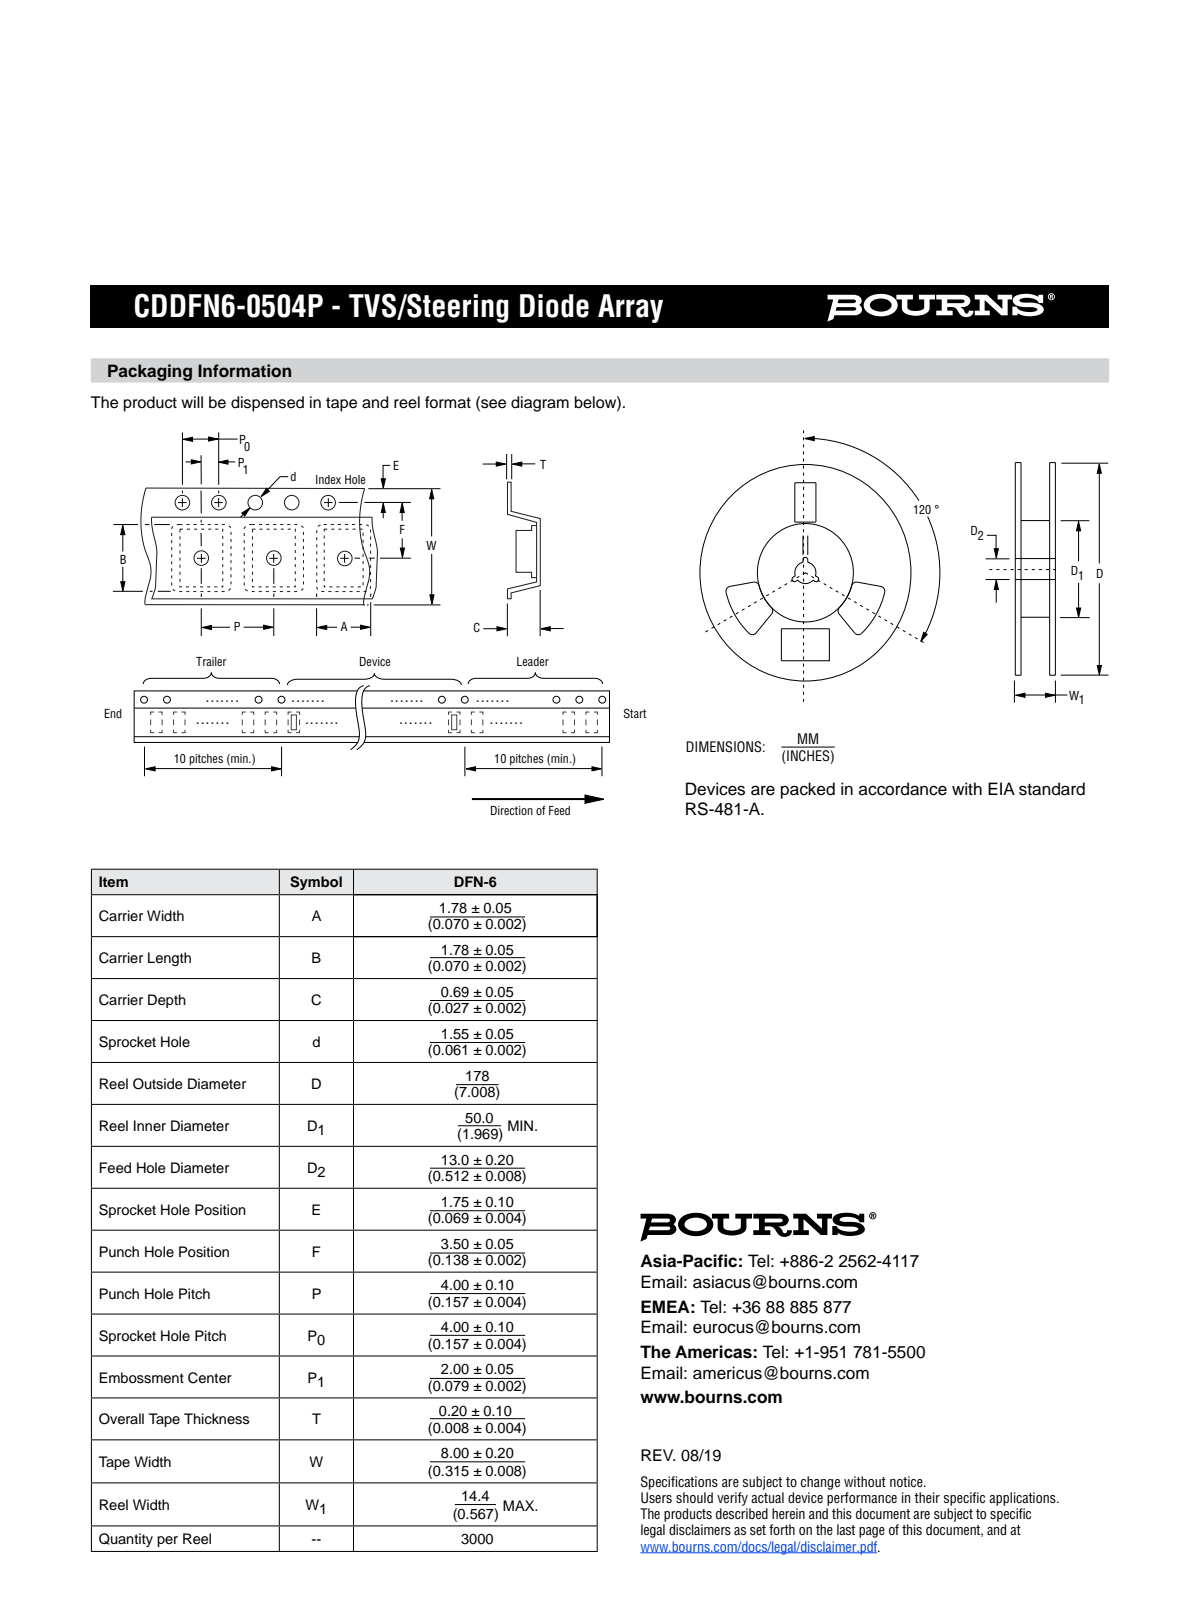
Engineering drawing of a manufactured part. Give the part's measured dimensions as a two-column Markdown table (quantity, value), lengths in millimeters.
| quantity | value |
| --- | --- |
| part name | CDDFN6-0504P |
| STEP written by | PRO/ENGINEER BY PARAMETRIC TECHNOLOGY CORPORATION, 2010100 (CONFIG_CONTROL_DESIGN) |
| units | millimeters |
| bodies | 1 solid, 50 faces (34 planar, 16 cylindrical, 0 other) |
| overall size | 1.6 × 1.6 × 0.55 |
| volume | 1 mm³ |
| surface area | 9 mm² |
| main face-to-face distances | 1.6, 0.5, 0.55, 1.1, 1.35, 0.68, 0.92, 0.43, 0.67, 0.85 |
